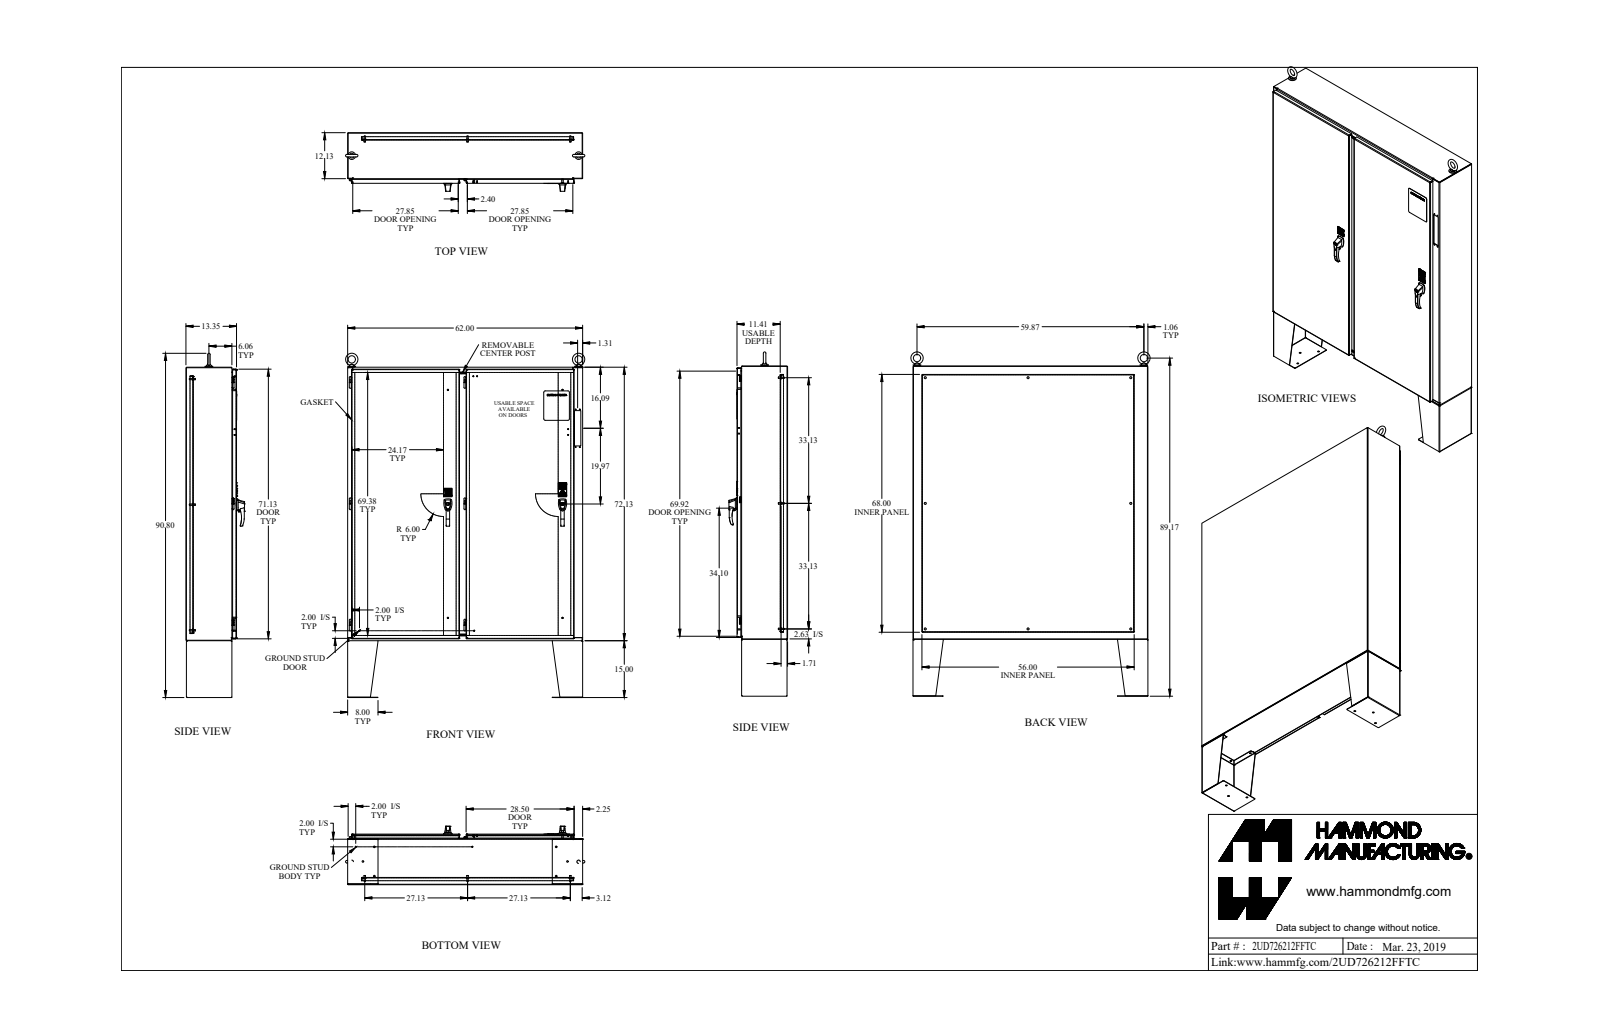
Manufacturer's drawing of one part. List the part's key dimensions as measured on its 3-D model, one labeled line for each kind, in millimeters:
Part name (STEP PRODUCT): 2UD726212FFTC
STEP written by: SolidWorks 2018 (AUTOMOTIVE_DESIGN)
Units: millimetres
Bodies: 214 solids, 3338 faces (1892 planar, 958 cylindrical, 488 other)
Overall size (bounding box): 2306.3 × 1603.3 × 392.8
Volume: 65 370 000 mm³ · Surface area: 26 790 000 mm²
Round holes (diameter × count): ⌀11.1 ×14, ⌀7.1 ×11, ⌀7.8 ×11, ⌀5 ×10, ⌀6.4 ×10, ⌀8.9 ×8, ⌀6.5 ×6, ⌀8 ×6, ⌀11.3 ×5, ⌀7.1 ×4, ⌀7.2 ×4, ⌀9.5 ×4
Round bosses / shafts (diameter × count): ⌀6.4 ×19, ⌀25.4 ×14, ⌀16.5 ×9, ⌀9.5 ×9, ⌀8.4 ×9, ⌀7.1 ×8, ⌀19.1 ×6, ⌀13.5 ×6
Partial cylindrical surfaces — rounded edges, fillets, slot ends (radius × count): R3.2 ×62, R1.5 ×51, R12.7 ×38, R0.4 ×32, R4.7 ×30, R0.8 ×28, R1.2 ×20, R3.6 ×20
Main face-to-face distances: 3.2, 1.8, 264.9, 339.5, 336.4, 74.6, 71.4, 72.8, 69.6, 266.8
Hole centre spacings: 768.4, 25.4, 32.7, 124.2, 128.9, 155.6, 253.1, 735
